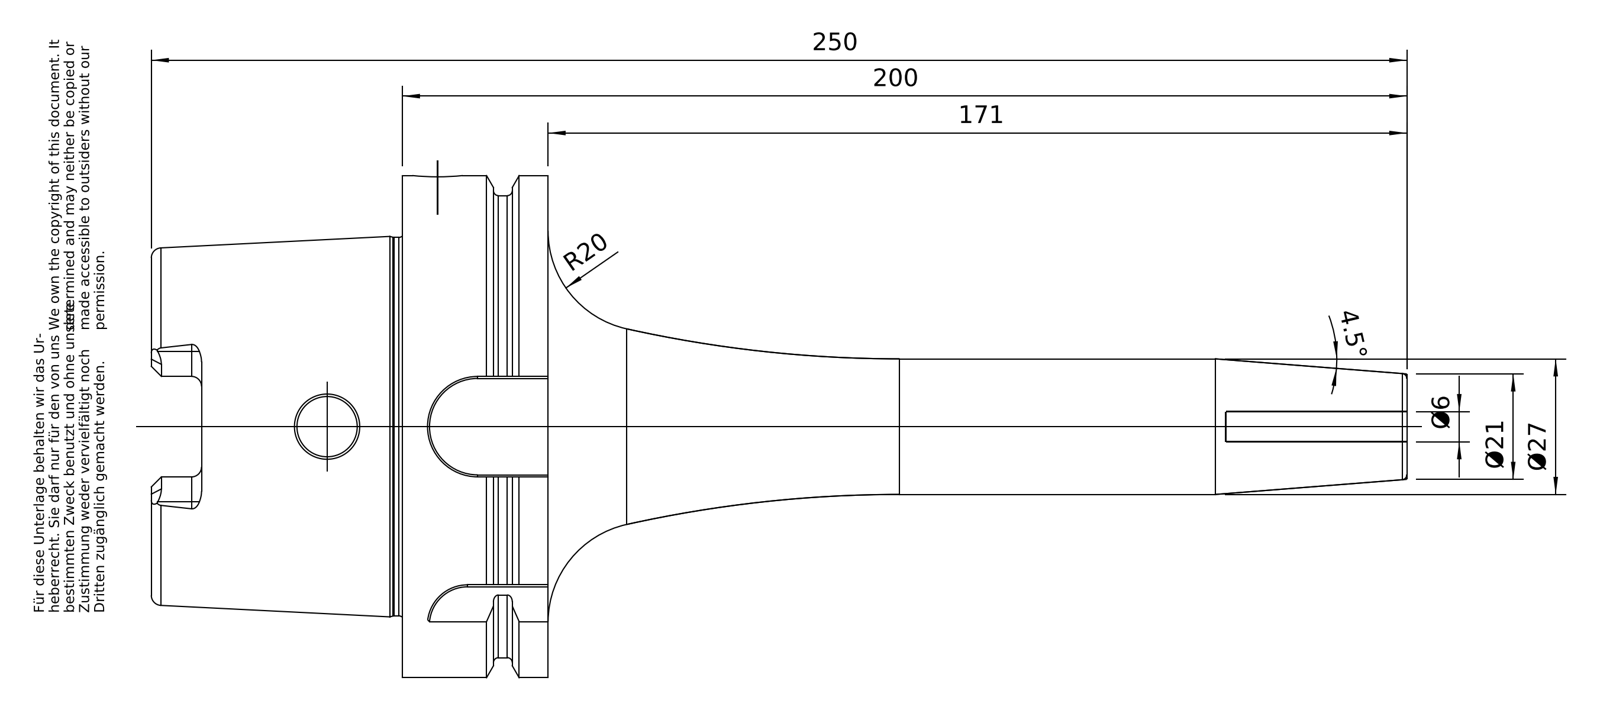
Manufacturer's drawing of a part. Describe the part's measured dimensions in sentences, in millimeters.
The part is named "A100-146-06". Its 3-D file was written by "PRO/ENGINEER BY PARAMETRIC TECHNOLOGY CORPORATION, 2010430 (CONFIG_CONTROL_DESIGN)". It is 1 solid with 176 faces: 50 planar, 51 cylindrical and 75 other. Overall it measures 250 by 100 by 100 millimeters. Its volume is 378 317 cubic millimeters and its surface area 64 667 square millimeters. Round holes: 1 of diameter 6, 1 of diameter 10, 1 of diameter 12, 1 of diameter 22.5, 1 of diameter 24, 1 of diameter 24.32, 1 of diameter 24.5, 1 of diameter 53, 1 of diameter 63. Round bosses or shafts: 1 of diameter 100, 1 of diameter 92, 1 of diameter 75.36, 1 of diameter 27. Partial cylindrical surfaces (rounded edges, fillets, slot ends): 6 of radius 2, 4 of radius 5, 1 of radius 8, 1 of radius 10, 1 of radius 11. The main face-to-face distances are 29, 12.5, 16.5, 50, 62.5, 79, 88, 78.5, 28.5, 16.
